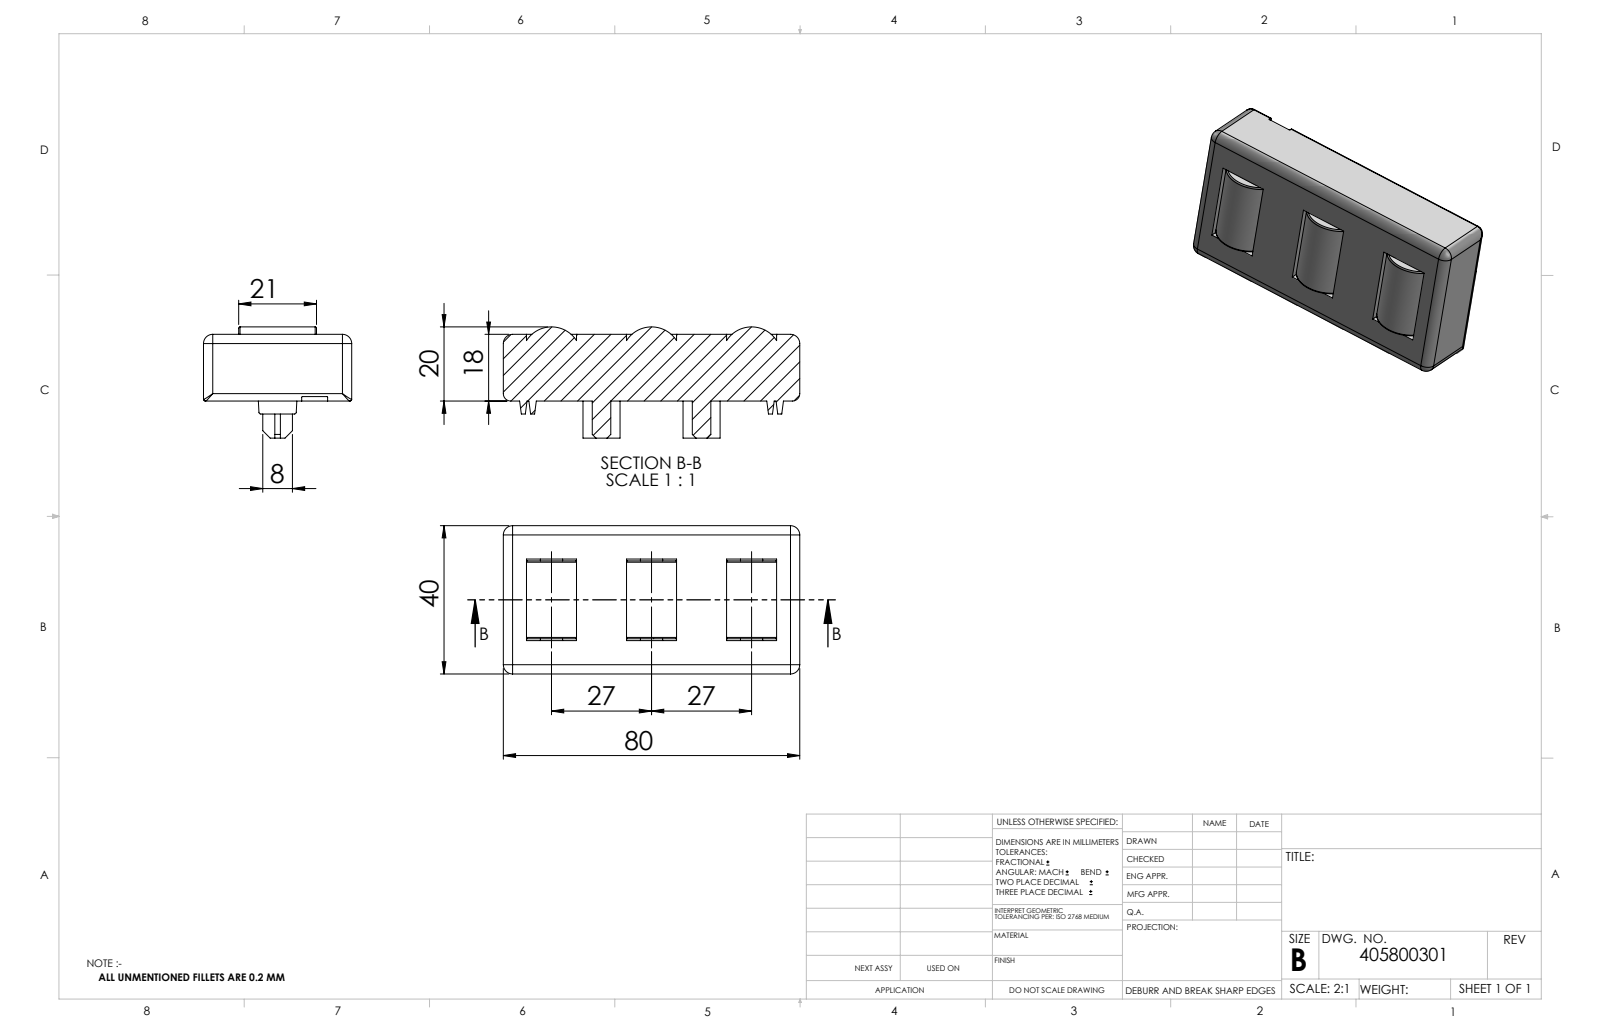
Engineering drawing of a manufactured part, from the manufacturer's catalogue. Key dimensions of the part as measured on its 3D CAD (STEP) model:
Part name (STEP PRODUCT): 405800301_c_1
STEP written by: SolidWorks 2014 (CONFIG_CONTROL_DESIGN)
Units: millimetres
Bodies: 1 solid, 169 faces (98 planar, 47 cylindrical, 24 other)
Overall size (bounding box): 80 × 40 × 30
Volume: 59 326 mm³ · Surface area: 12 160 mm²
Partial cylindrical surfaces — rounded edges, fillets, slot ends (radius × count): R2.5 ×10, R0.2 ×8, R0.5 ×6, R5 ×3, R8 ×3, R2 ×2
Main face-to-face distances: 18, 40, 80, 16, 24, 21.5, 11.75, 27, 4.75, 6.5
